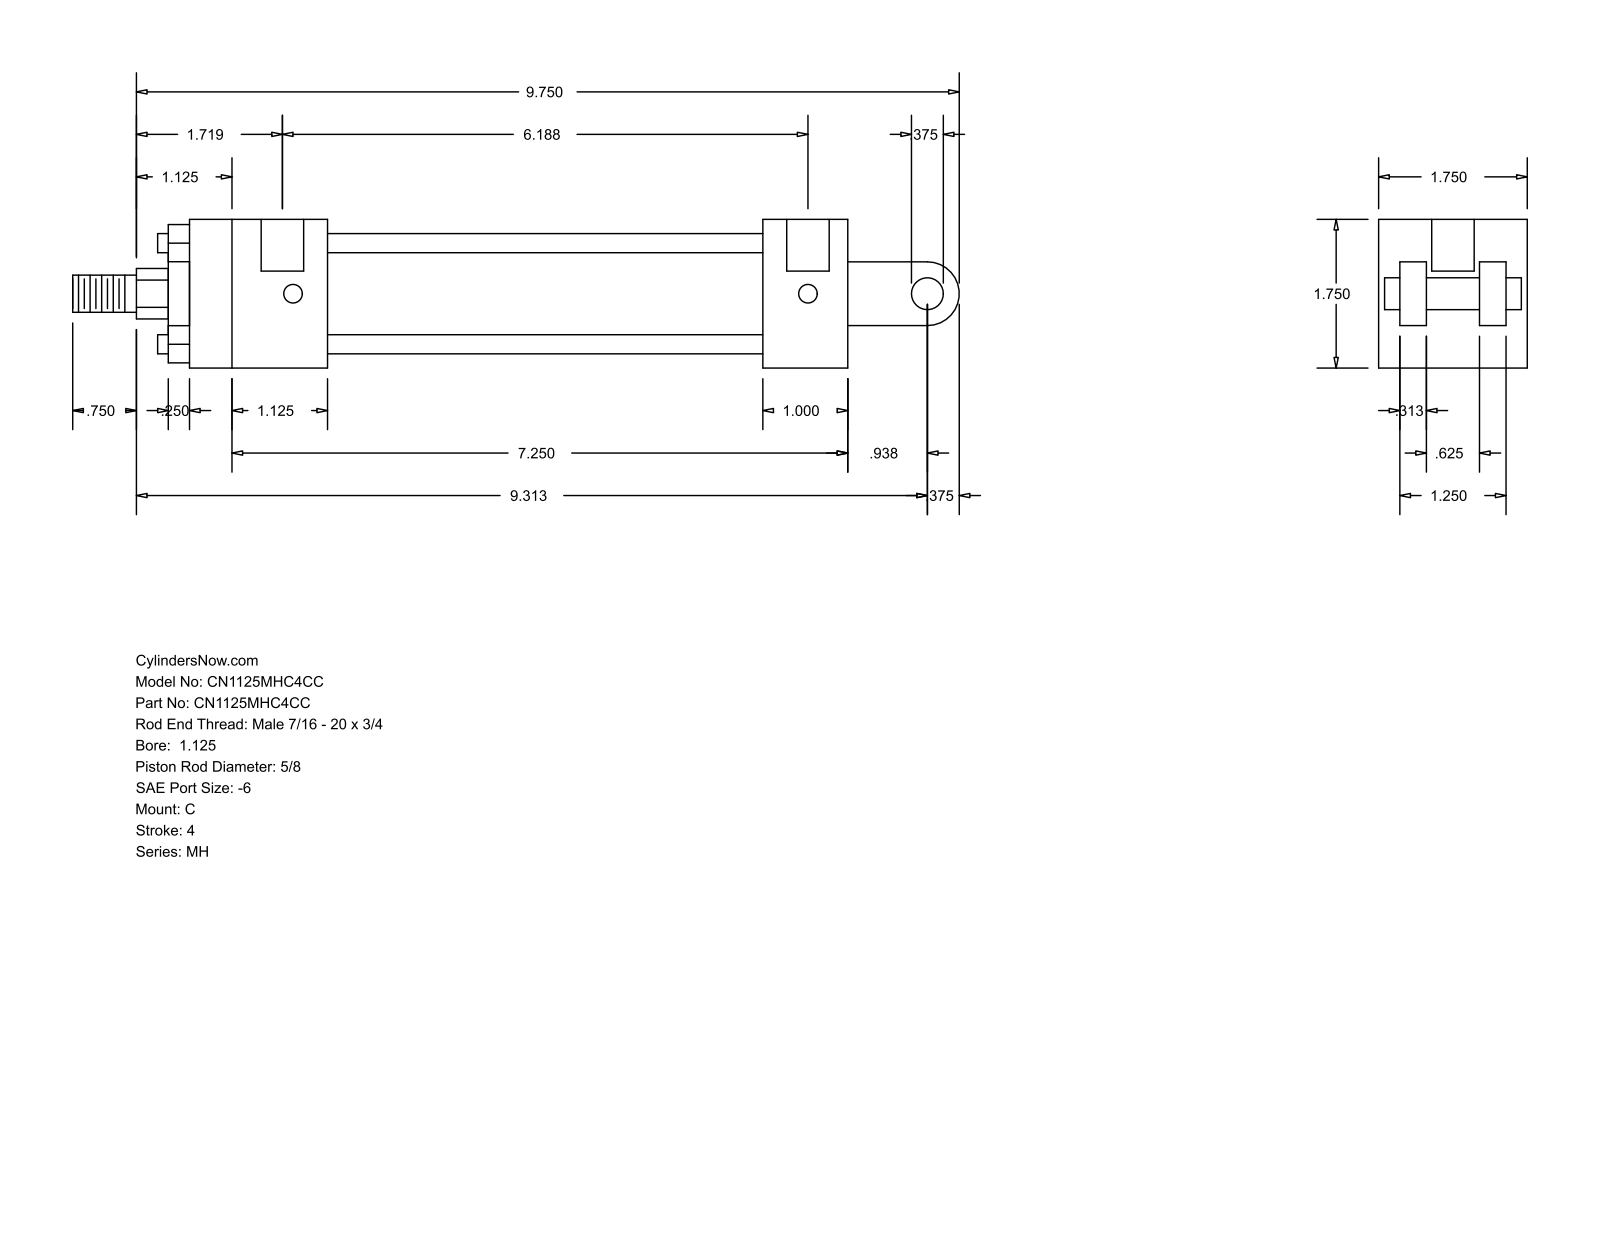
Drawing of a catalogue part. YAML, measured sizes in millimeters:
part_name: "MH_C__0112_0.625"
step_written_by: "GSSL Pune (CONFIG_CONTROL_DESIGN)"
units: millimeters
bodies: {solids: 0, faces: 99, planar: 70, cylindrical: 29, other: 0}
overall_size: [265.11, 44.45, 44.45]
round_holes:
  - {diameter: 5.56, count: 4}
  - {diameter: 12.7, count: 2}
round_bosses_or_shafts:
  - {diameter: 5.71, count: 4}
  - {diameter: 34.92, count: 1}
  - {diameter: 28.57, count: 1}
  - {diameter: 15.88, count: 1}
  - {diameter: 11.11, count: 1}
  - {diameter: 9.53, count: 1}
partial_cylinders:
  - {radius: 7.54, count: 1}
  - {radius: 9.53, count: 1}
face_to_face_distances: [44.46, 6.35, 31.76, 14.29, 25.4, 30.17, 38.11, 7.94, 23.82, 12.7]
hole_center_spacings: [153.99, 3.17, 157.16]
